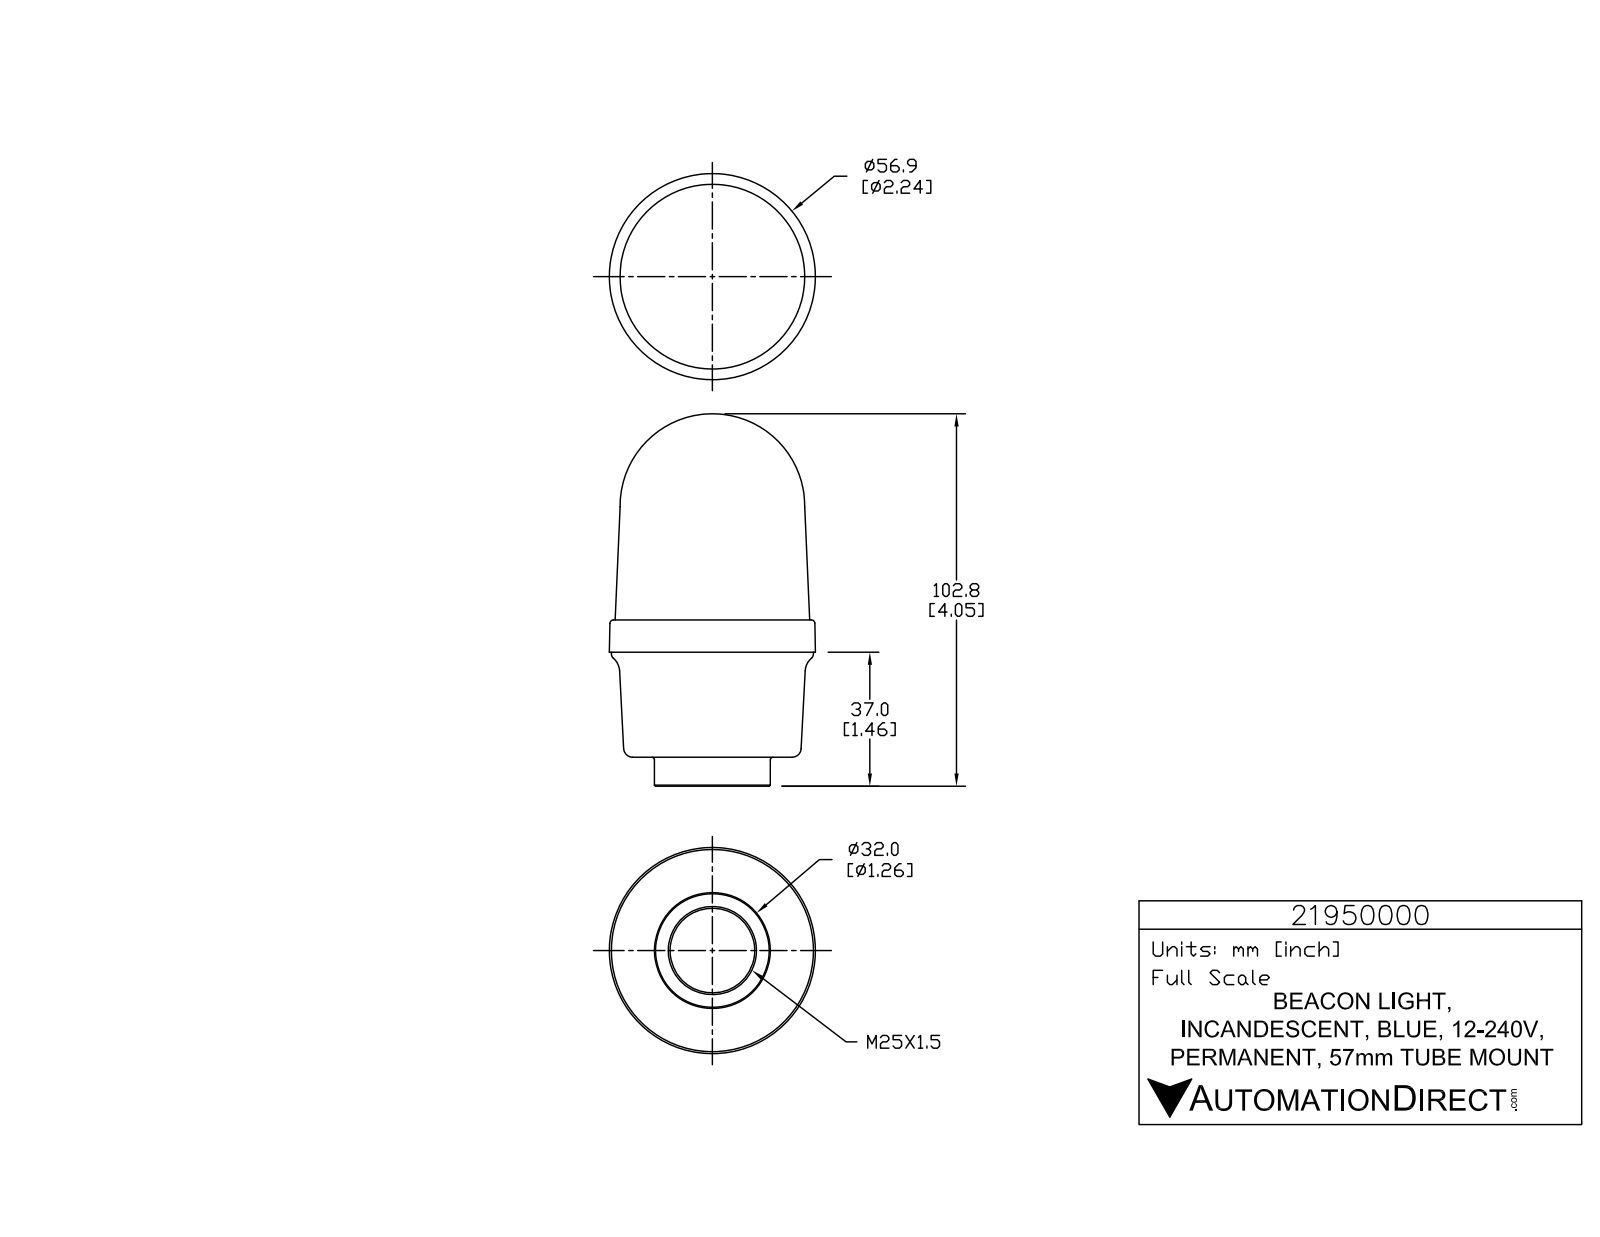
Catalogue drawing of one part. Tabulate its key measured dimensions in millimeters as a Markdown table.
| quantity | value |
| --- | --- |
| part name | 21950000 |
| STEP written by | SolidWorks 2015 (AUTOMOTIVE_DESIGN) |
| units | millimeters |
| bodies | 1 solid, 764 faces (524 planar, 145 cylindrical, 95 other) |
| overall size | 102.8 × 56.9 × 56.9 |
| volume | 186 111 mm³ |
| surface area | 18 965 mm² |
| round holes (diameter × count) | 0.99 × 3, 23.38 × 1 |
| round bosses / shafts (diameter × count) | 5.74 × 3, 1.43 × 3, 55.8 × 1, 32 × 1 |
| partial cylindrical surfaces (radius × count) | 0.2 × 6, 0.21 × 6, 0.21 × 6, 3.32 × 6, 0.1 × 3, 0.12 × 3, 0.19 × 3, 0.2 × 3 |
| main face-to-face distances | 8, 29, 37, 8.9, 37.9, 45.9, 10.61, 19.51, 48.51, 56.51 |
